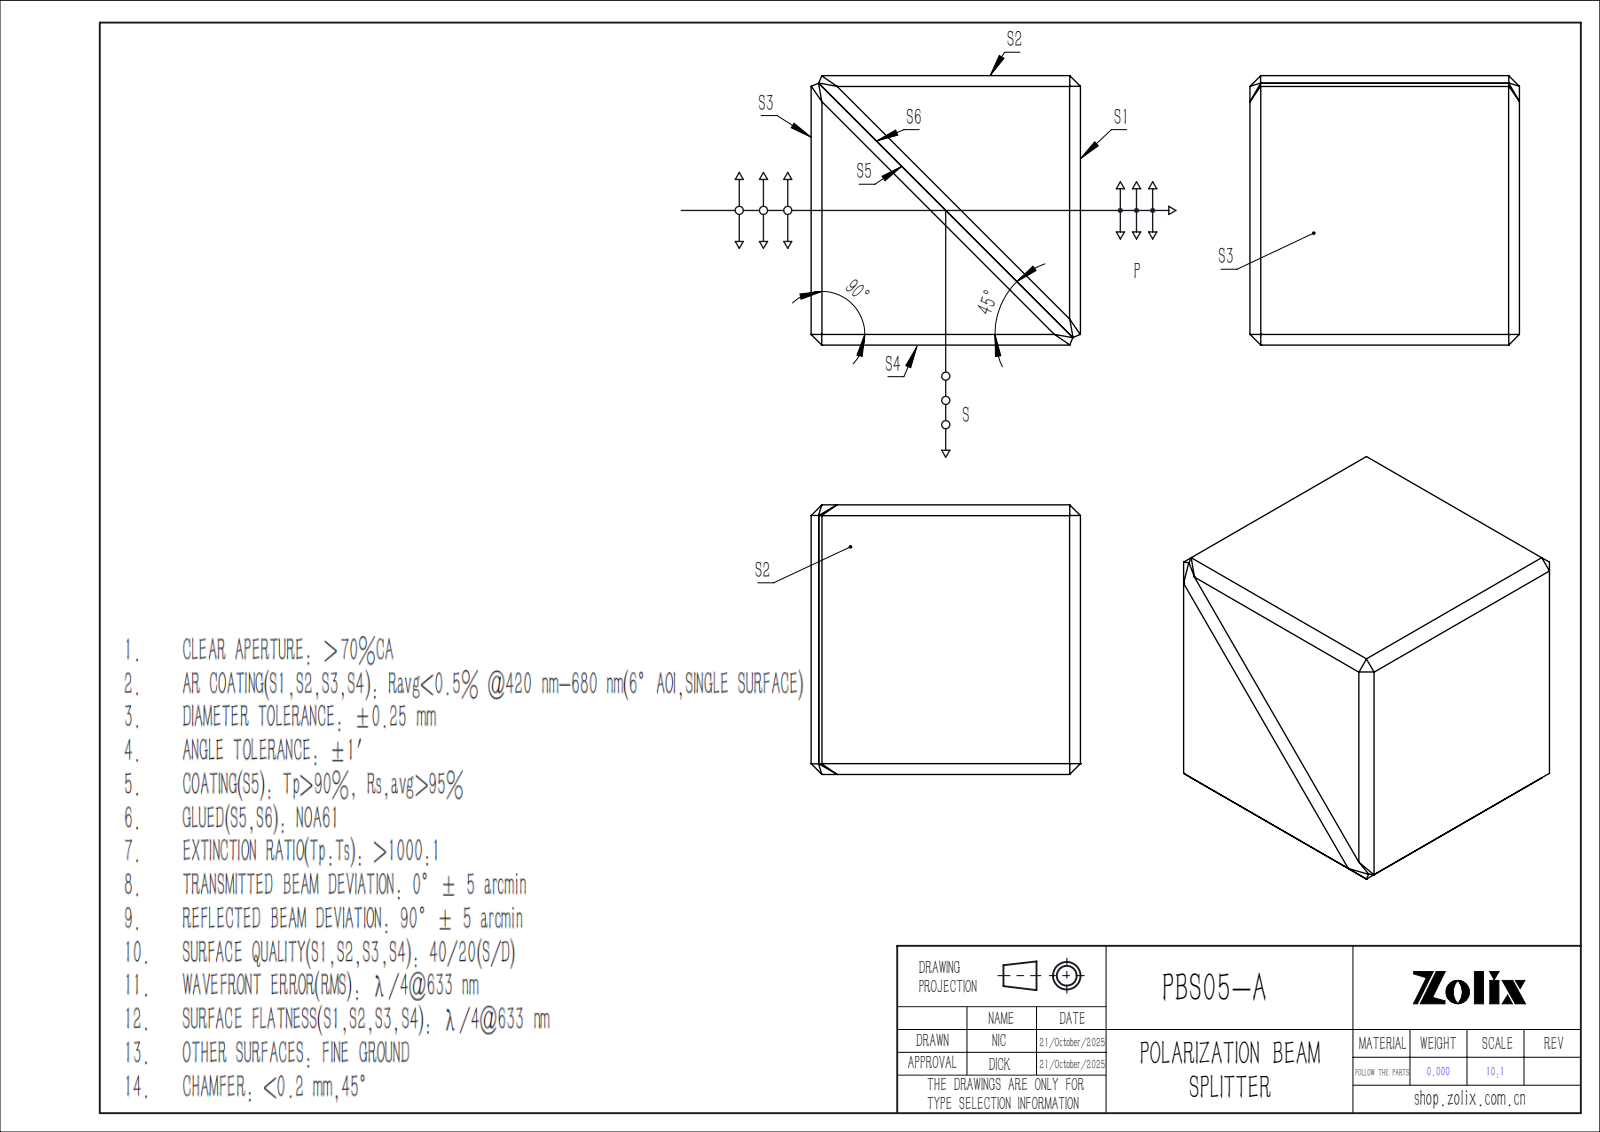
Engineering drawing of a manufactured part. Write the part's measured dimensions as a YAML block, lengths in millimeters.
part_name: "PBS601-1; PBS601; PBS601-2"
step_written_by: "SolidWorks 2022 (CONFIG_CONTROL_DESIGN)"
units: millimeters
bodies: {solids: 2, faces: 43, planar: 41, cylindrical: 2, other: 0}
overall_size: [5, 5, 5]
volume: 123
surface_area: 206
round_holes:
  - {diameter: 0.2, count: 1}
face_to_face_distances: [5, 6.79, 3.25, 3.39, 6.78, 6.16, 6.17, 7.08, 8.2, 8.19]
